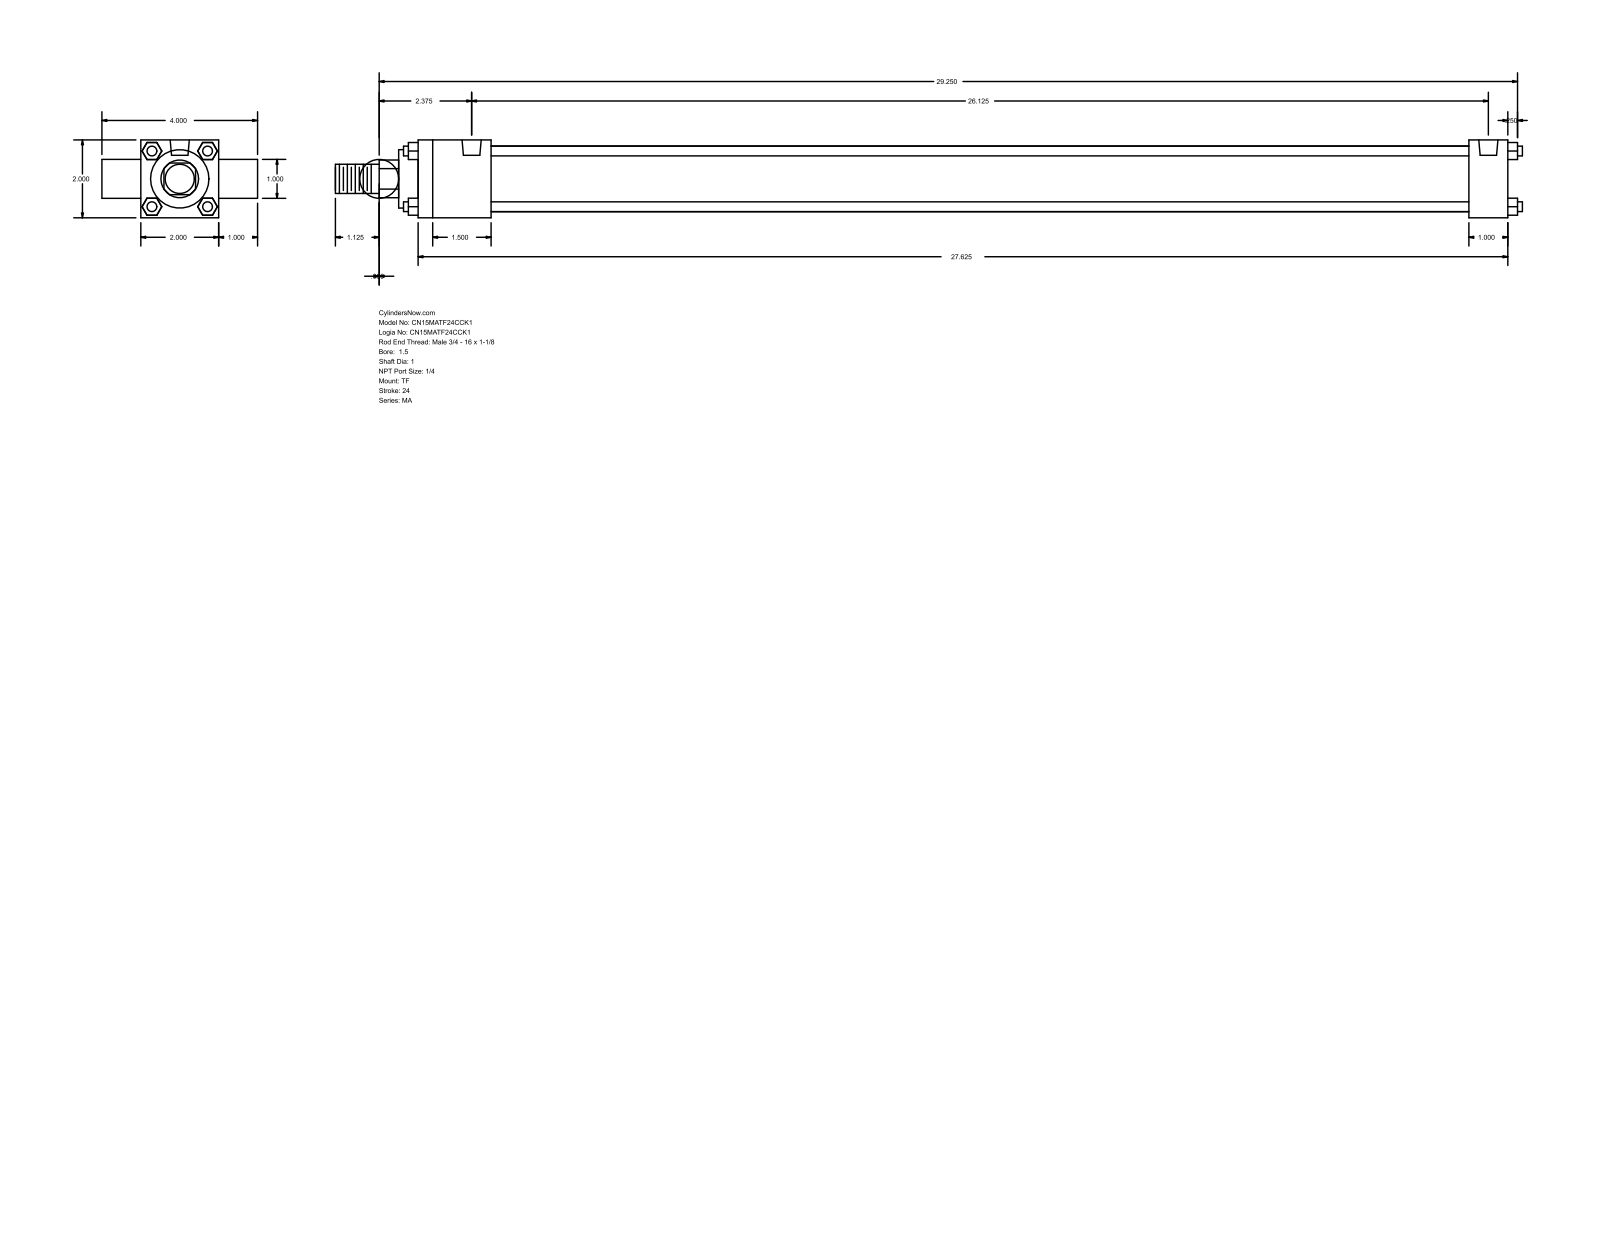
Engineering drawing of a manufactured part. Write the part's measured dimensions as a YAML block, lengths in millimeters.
part_name: "MA_TF__0150_1"
step_written_by: "GSSL Pune (CONFIG_CONTROL_DESIGN)"
units: millimeters
bodies: {solids: 0, faces: 120, planar: 92, cylindrical: 28, other: 0}
overall_size: [774.7, 101.6, 50.8]
round_holes:
  - {diameter: 7.94, count: 3}
  - {diameter: 12.49, count: 2}
round_bosses_or_shafts:
  - {diameter: 6.35, count: 4}
  - {diameter: 25.4, count: 2}
  - {diameter: 42.93, count: 1}
  - {diameter: 38.1, count: 1}
  - {diameter: 19.05, count: 1}
partial_cylinders:
  - {radius: 12.29, count: 1}
face_to_face_distances: [50.8, 25.4, 711.2, 76.2, 6.35, 47.63, 685.8, 638.17, 663.57, 723.9]
hole_center_spacings: [663.57]
